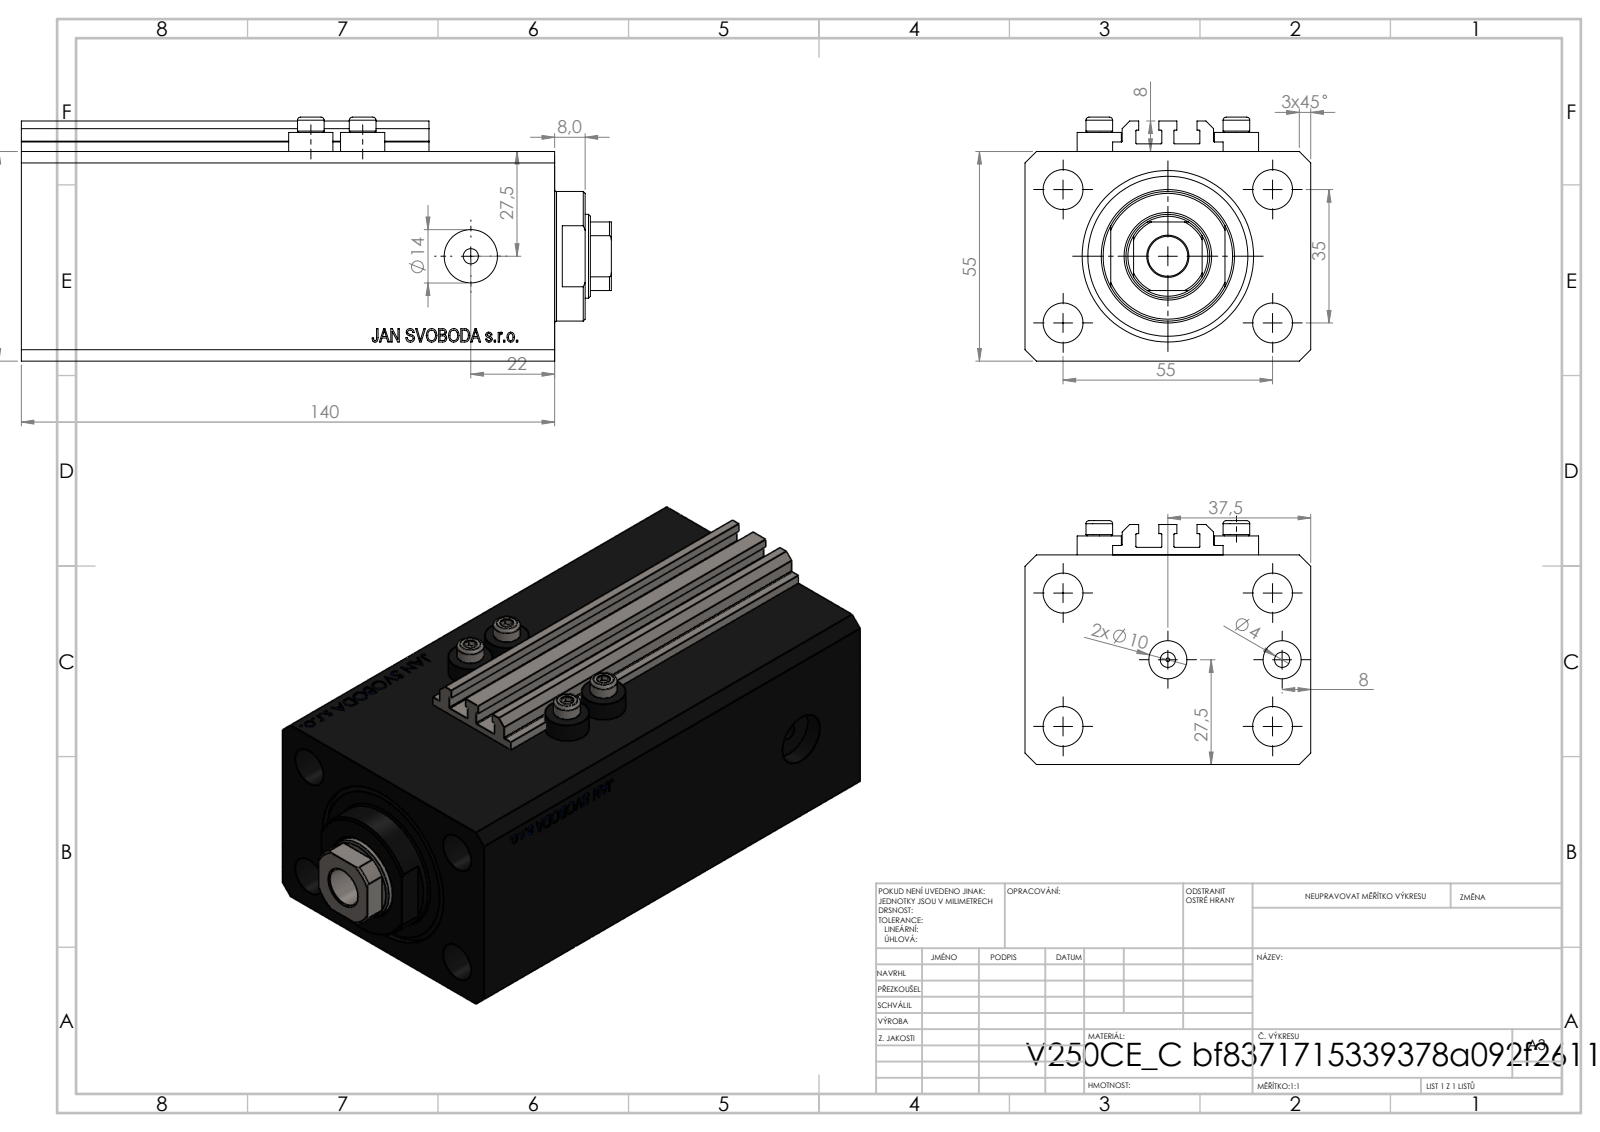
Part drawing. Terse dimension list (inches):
name: ALLEN BOLT V250CE; V250CE_C_VCP; V250CE_VC_C; V250CE_C_Body
written by: SolidWorks 2019 (CONFIG_CONTROL_DESIGN)
unit: in
bodies: 8 solids, 1038 faces (504 planar, 88 cylindrical, 446 other)
size: 6.098 × 2.953 × 2.52
volume: 31.27 in³; area: 176.5 in²
holes: 8× ⌀0.157, 5× ⌀0.413, 2× ⌀0.394, 2× ⌀0.551, 1× ⌀0.049, 1× ⌀0.866, 1× ⌀1.26, 1× ⌀1.772
bosses: 4× ⌀0.457, 4× ⌀0.276, 1× ⌀1.339
rounds: 10× R0.008, 1× R0.413
face distances: 2.165, 2.953, 5.512, 4.445, 1.067, 0.39, 4.055, 5.122, 0.315, 0.098
hole spacings: 1.283, 0.535, 0.696, 1.378, 1.417, 1.515, 2.165, 2.366
